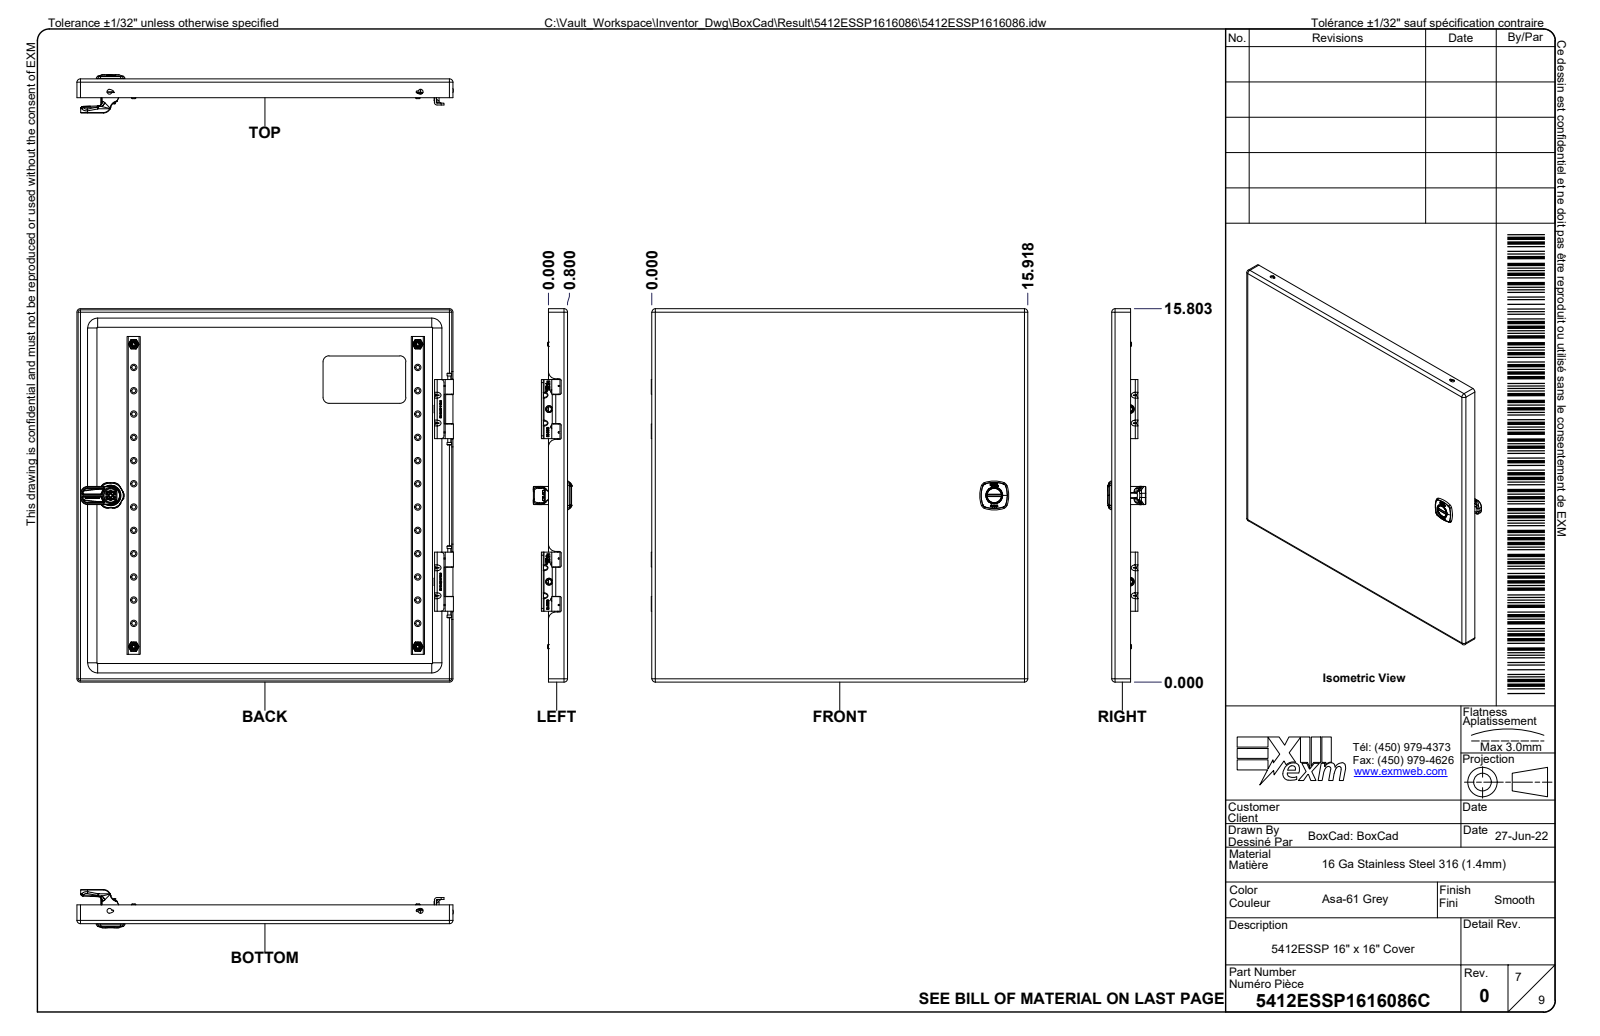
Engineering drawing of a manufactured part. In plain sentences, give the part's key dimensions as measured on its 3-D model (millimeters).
The part is named "5412ESSP1616086; 5412ESSP1616086B; 5412ESSP1616086B-P; STK-Q-16020 (+8 more)". Its 3-D file was written by "Autodesk Inventor 2024 (AUTOMOTIVE_DESIGN)". It is 56 solids with 7573 faces: 2187 planar, 1718 cylindrical and 3668 other. Overall it measures 406.4 by 406.4 by 236.4 millimeters. Its volume is 1 485 000 cubic millimeters and its surface area 1 913 000 square millimeters. Round holes: 24 of diameter 4.2, 9 of diameter 0.8, 8 of diameter 8, 7 of diameter 5.1, 6 of diameter 7.4, 5 of diameter 7.9, 4 of diameter 1.1, 4 of diameter 5, 4 of diameter 6.8, 4 of diameter 6.9, 4 of diameter 9.9, 2 of diameter 6. Round bosses or shafts: 24 of diameter 6, 9 of diameter 0.8, 8 of diameter 5.9, 8 of diameter 1, 4 of diameter 18.2, 4 of diameter 9.5, 4 of diameter 7.9, 4 of diameter 6.7. Partial cylindrical surfaces (rounded edges, fillets, slot ends): 78 of radius 0.5, 56 of radius 1, 54 of radius 0.2, 26 of radius 0.8, 24 of radius 2.1, 18 of radius 0.3, 16 of radius 0.3, 16 of radius 3.2. The main face-to-face distances are 1.3, 405.1, 230.7, 229.3, 406.4, 403.7, 232, 23.5, 22.2, 207.1. The hole center spacings are 25, 50, 75, 306.6, 100, 309.7, 314.7, 125.
